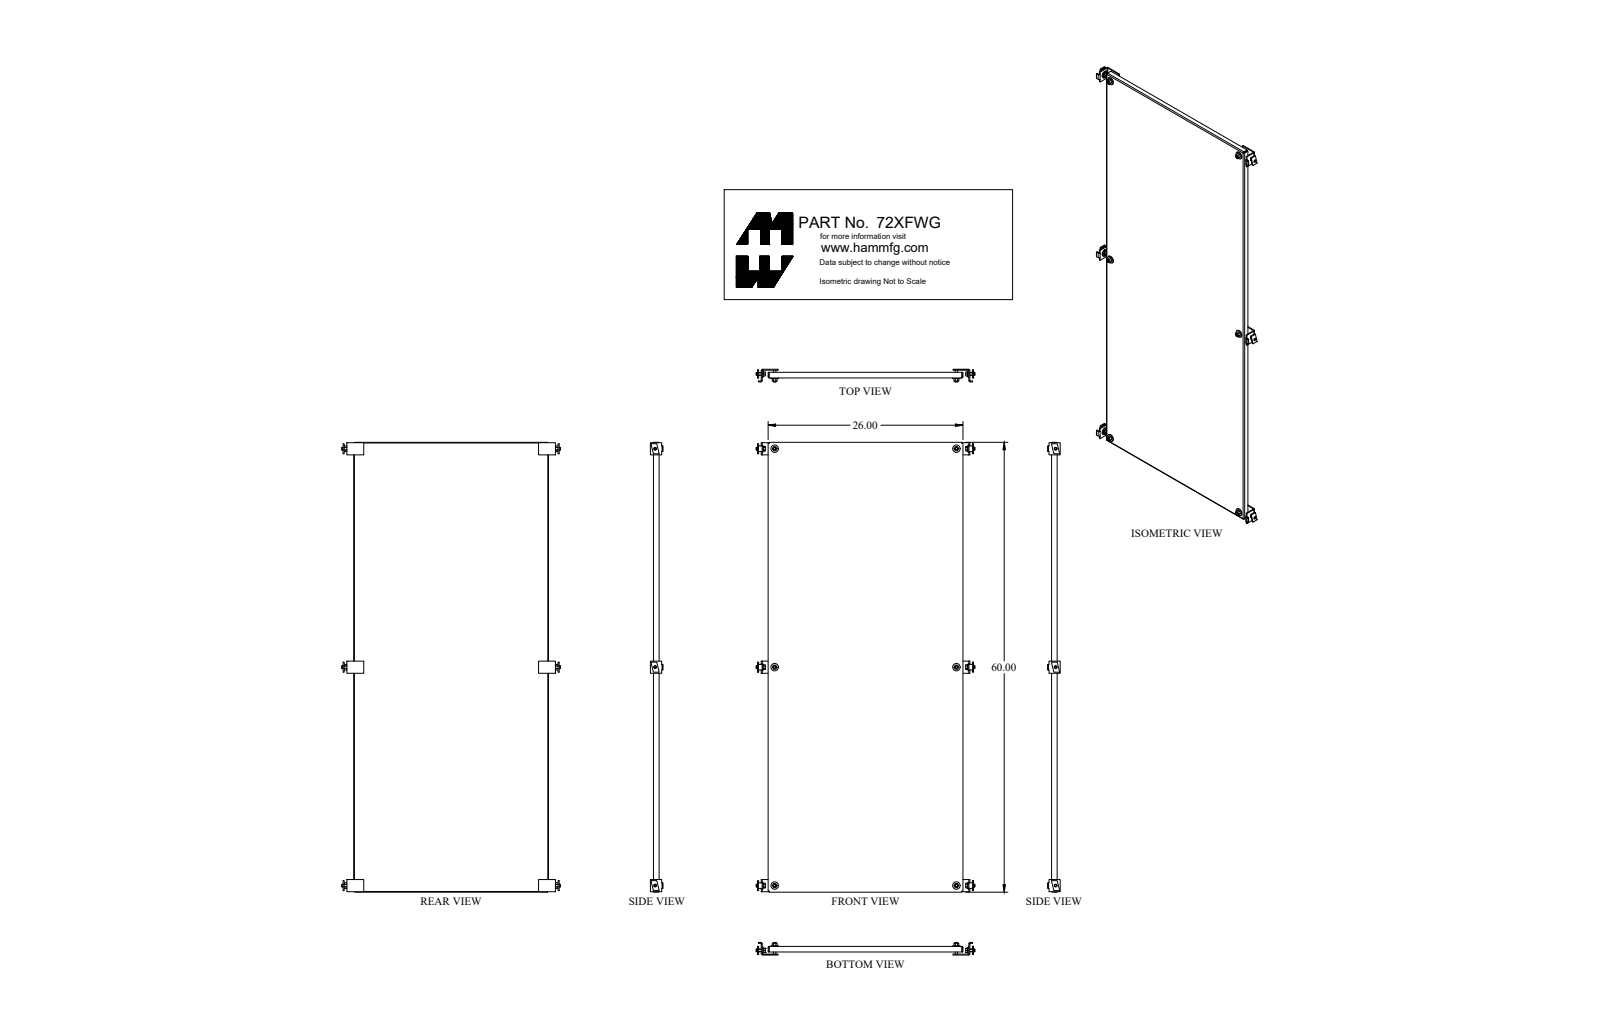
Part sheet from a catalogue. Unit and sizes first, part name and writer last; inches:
Units: inches
Overall size (bounding box): 60 × 28.582 × 1.687
Round holes (diameter × count): ⌀0.563 ×6, ⌀0.437 ×3
Round bosses / shafts (diameter × count): ⌀0.65 ×6, ⌀0.375 ×6, ⌀0.33 ×6
Partial cylindrical surfaces — rounded edges, fillets, slot ends (radius × count): R0.048 ×4, R0.06 ×4, R0.143 ×4, R0.185 ×4
Main face-to-face distances: 0.095, 25.905, 25.81, 26, 0.125, 59.905, 1.032, 0.937, 1.157, 1.062
Hole centre spacings: 29.125, 37.898, 24.25, 29.13, 58.25, 63.096, 58.26
Volume: 163.6 in³ · Surface area: 3 441 in²
Bodies: 13 solids, 270 faces (130 planar, 92 cylindrical, 48 other)
Part name (STEP PRODUCT): 72XFWG_Default
STEP written by: SolidWorks 2018 (CONFIG_CONTROL_DESIGN)
